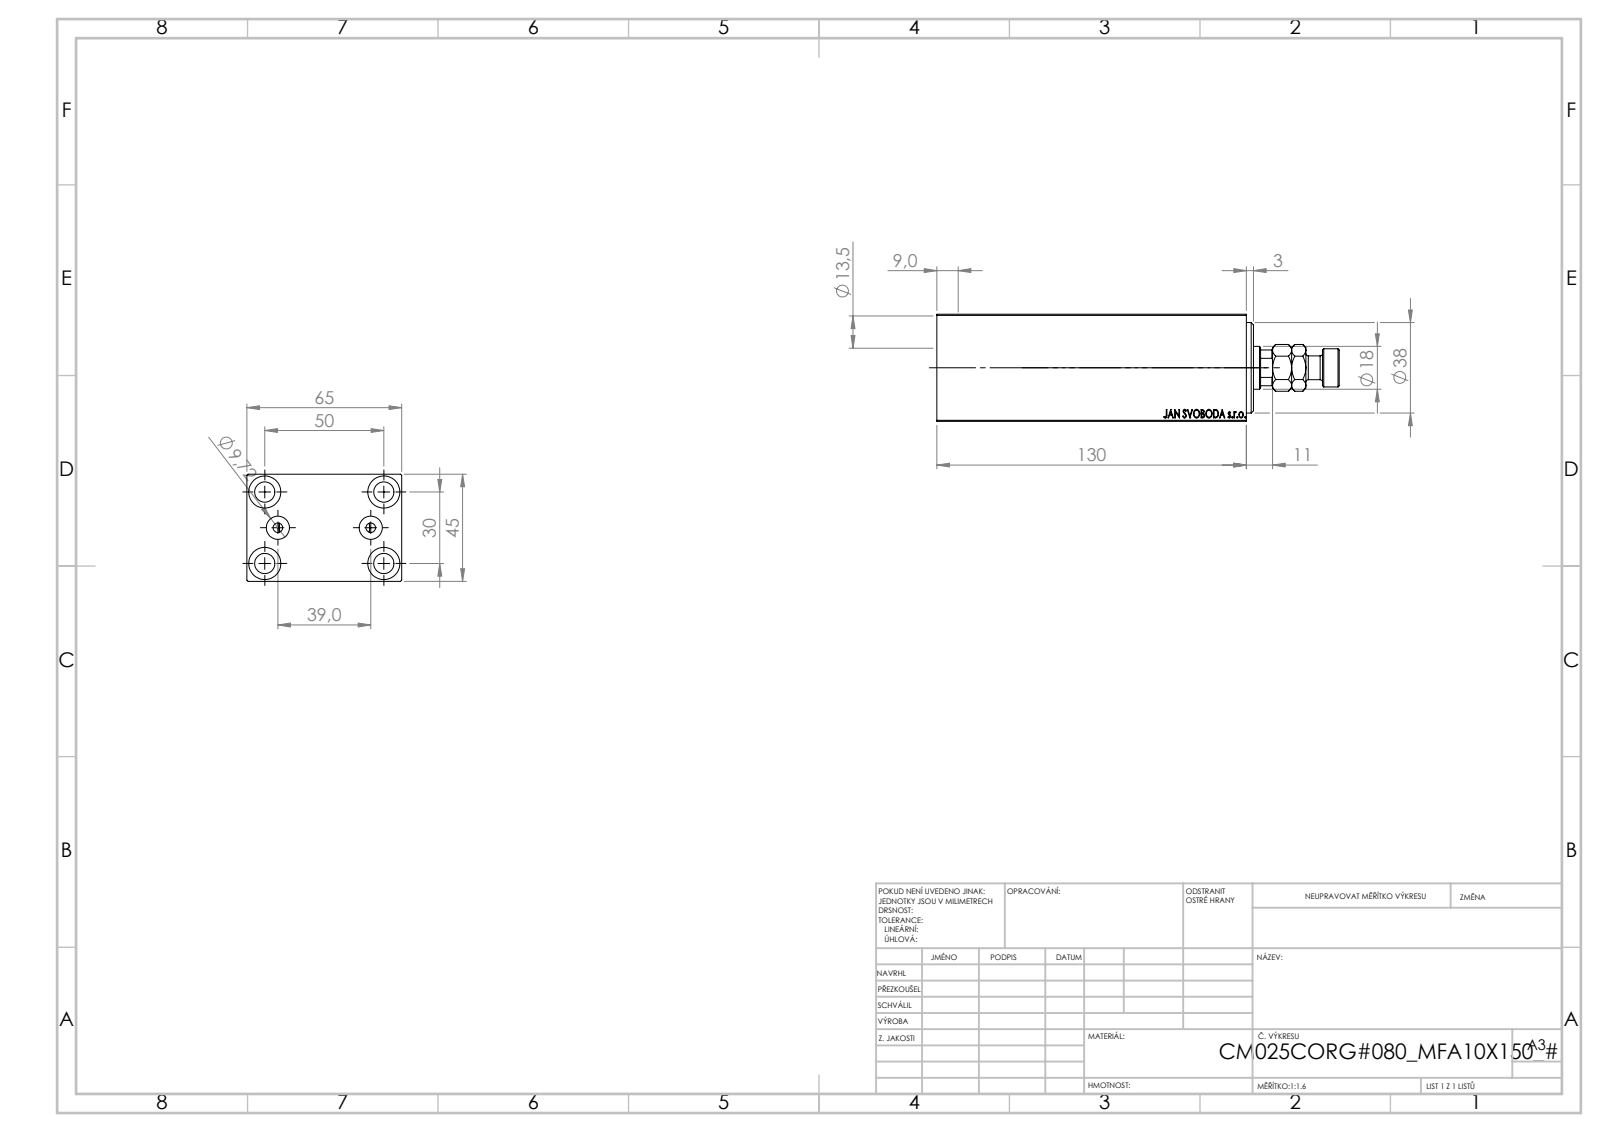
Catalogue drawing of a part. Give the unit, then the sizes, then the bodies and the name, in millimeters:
Units: millimetres
Overall size (bounding box): 169 × 65 × 45
Round holes (diameter × count): ⌀8.5 ×5, ⌀13.5 ×4, ⌀4 ×2, ⌀9.72 ×2, ⌀18 ×1, ⌀21.5 ×1, ⌀25 ×1, ⌀27 ×1, ⌀38 ×1
Round bosses / shafts (diameter × count): ⌀16 ×1, ⌀10 ×1
Partial cylindrical surfaces — rounded edges, fillets, slot ends (radius × count): R8.5 ×1
Main face-to-face distances: 45, 65, 124, 125, 5, 130, 3, 8, 6, 119
Hole centre spacings: 15.98, 29.15, 46.96, 19.5, 30, 50, 58.31, 39
Volume: 330 576 mm³ · Surface area: 79 719 mm²
Bodies: 4 solids, 910 faces (424 planar, 60 cylindrical, 426 other)
Part name (STEP PRODUCT): V450CM_C_VCP; MFA; V450CM_C_Body; V450CM_VC_B
STEP written by: SolidWorks 2019 (CONFIG_CONTROL_DESIGN)
